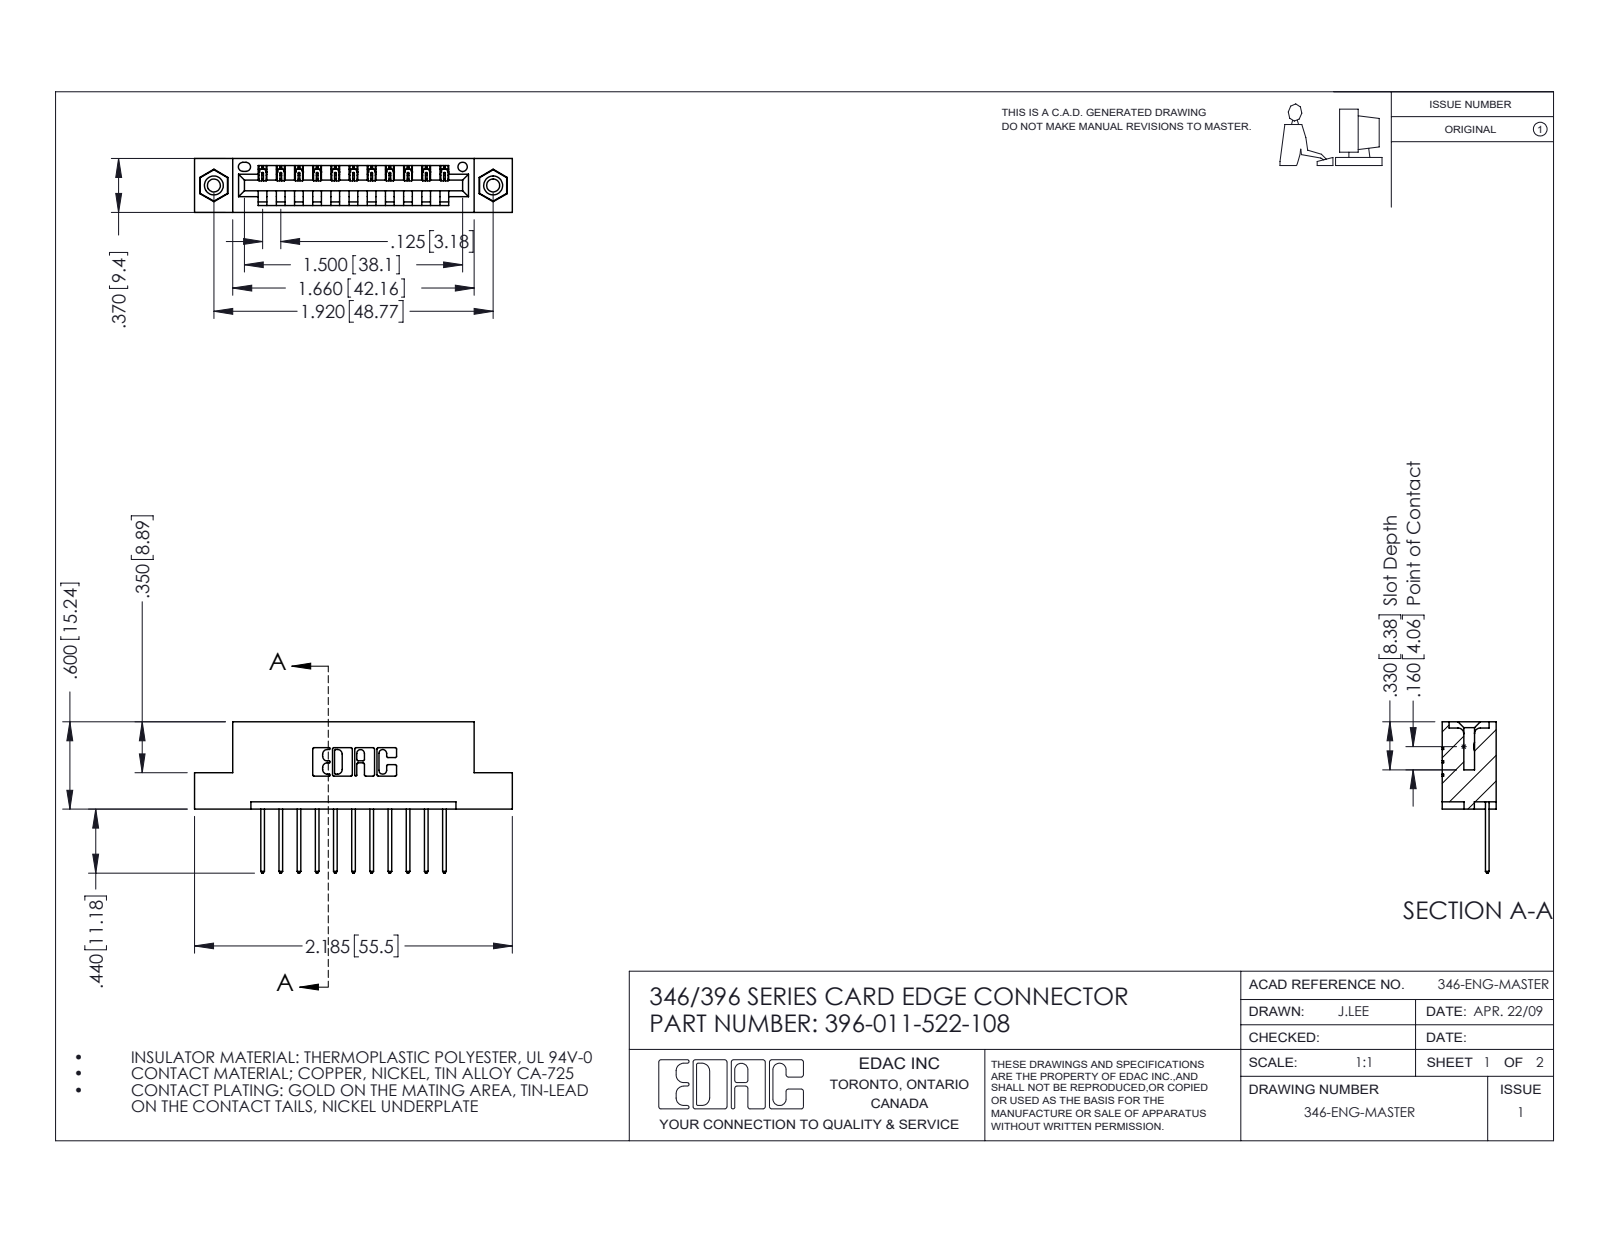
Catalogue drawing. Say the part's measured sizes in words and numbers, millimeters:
The part is named "345-250-001_345-250-003-102; 345-292-001_345-293-122; 346 Part_Flush Mounting Lugs - 0.156 Dia-TI; 396-011-522-108". Its 3-D file was written by "SolidWorks 2016 (CONFIG_CONTROL_DESIGN)". It is 14 solids with 820 faces: 548 planar, 256 cylindrical and 16 other. Overall it measures 55.5 by 26.4 by 9.4 millimeters. Its volume is 5 100 cubic millimeters and its surface area 6 094 square millimeters. Round holes: 2 of diameter 2.3, 2 of diameter 3.2, 2 of diameter 4, 1 of diameter 1.6. Round bosses or shafts: 2 of diameter 3.9. Partial cylindrical surfaces (rounded edges, fillets, slot ends): 22 of radius 0.2, 22 of radius 0.3, 22 of radius 0.3, 6 of radius 0.2, 6 of radius 0.8, 3 of radius 0.7, 2 of radius 0.8, 2 of radius 1. The main face-to-face distances are 6.4, 1.2, 8.2, 9.4, 1.8, 7.6, 0.6, 3.8, 5.6, 2.5. The hole center spacings are 6.2, 43.6, 48.8.
